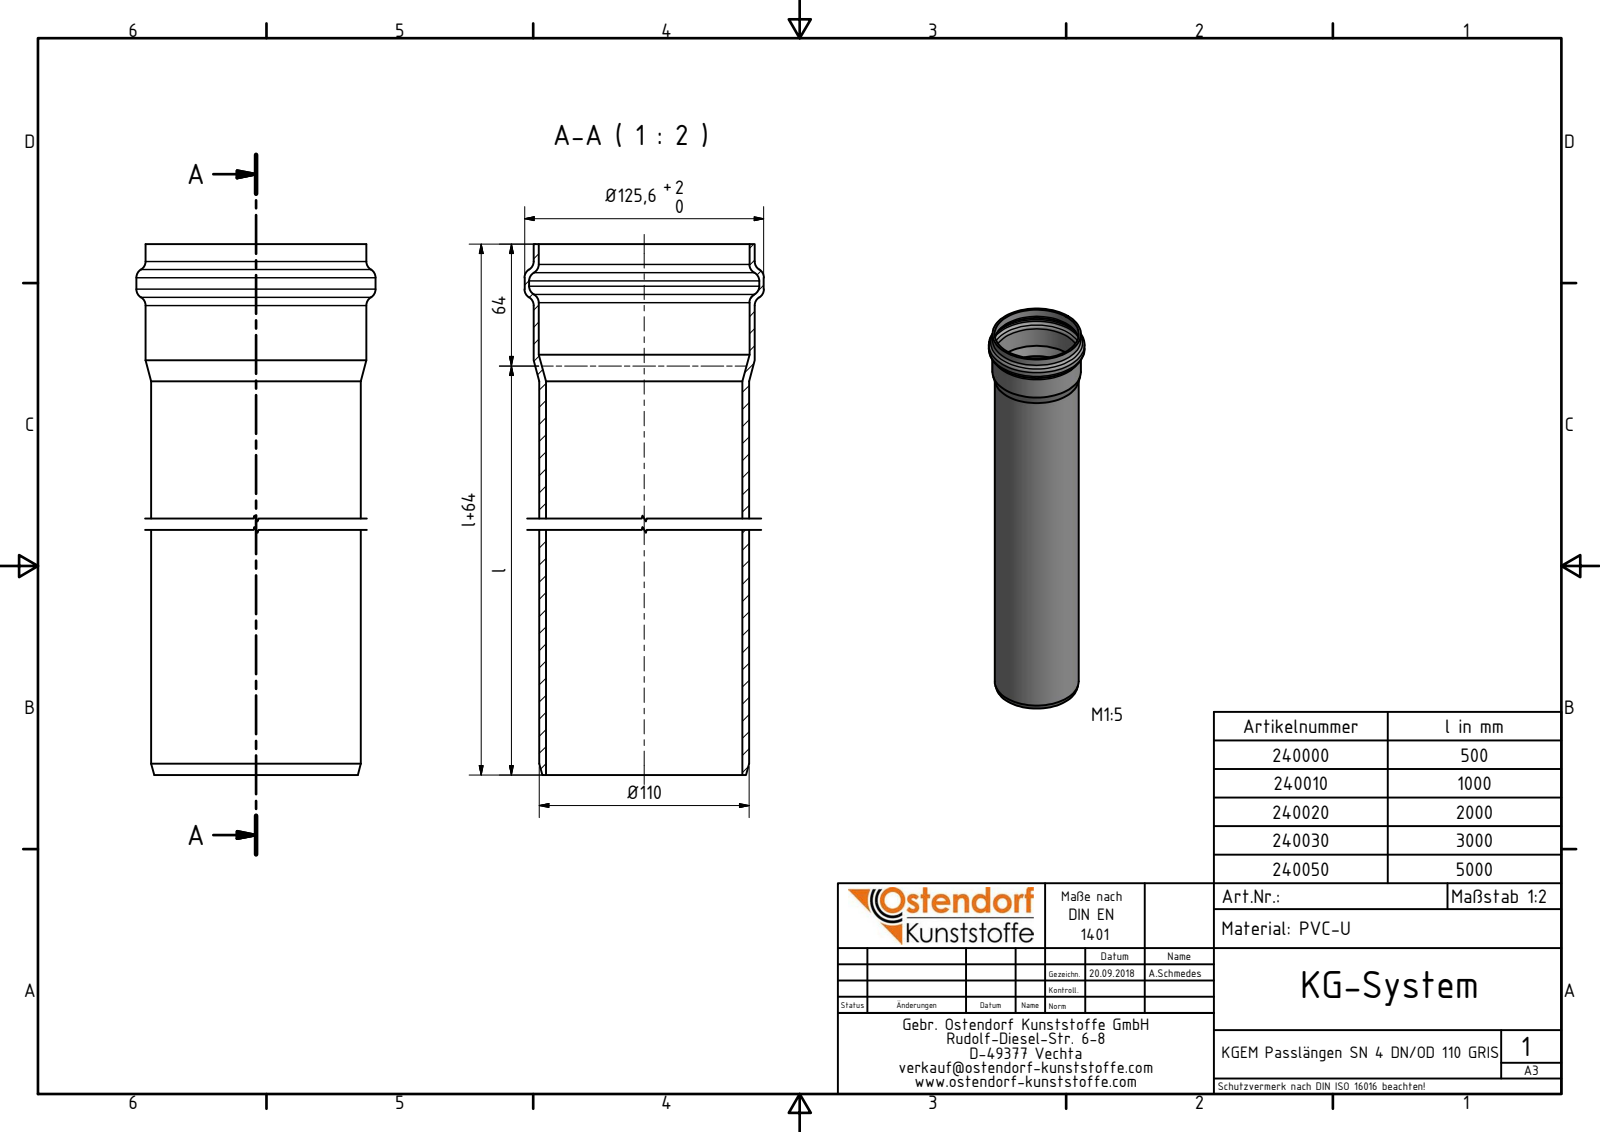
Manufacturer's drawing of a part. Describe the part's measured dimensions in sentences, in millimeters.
The part is named "240000 KGEM Passlängen SN 4 DN_OD 110x500 GRIS". Its 3-D file was written by "Autodesk Inventor 2016 (AUTOMOTIVE_DESIGN)". It is 1 solid with 21 faces: 2 planar, 8 cylindrical and 11 other. Overall it measures 564 by 125.6 by 125.6 millimeters. Its volume is 652 851 cubic millimeters and its surface area 386 062 square millimeters. Round holes: 1 of diameter 103.15, 1 of diameter 110.65, 1 of diameter 120.8. Round bosses or shafts: 1 of diameter 125.6, 1 of diameter 116.05, 1 of diameter 110.15. The main face-to-face distances are 564.
